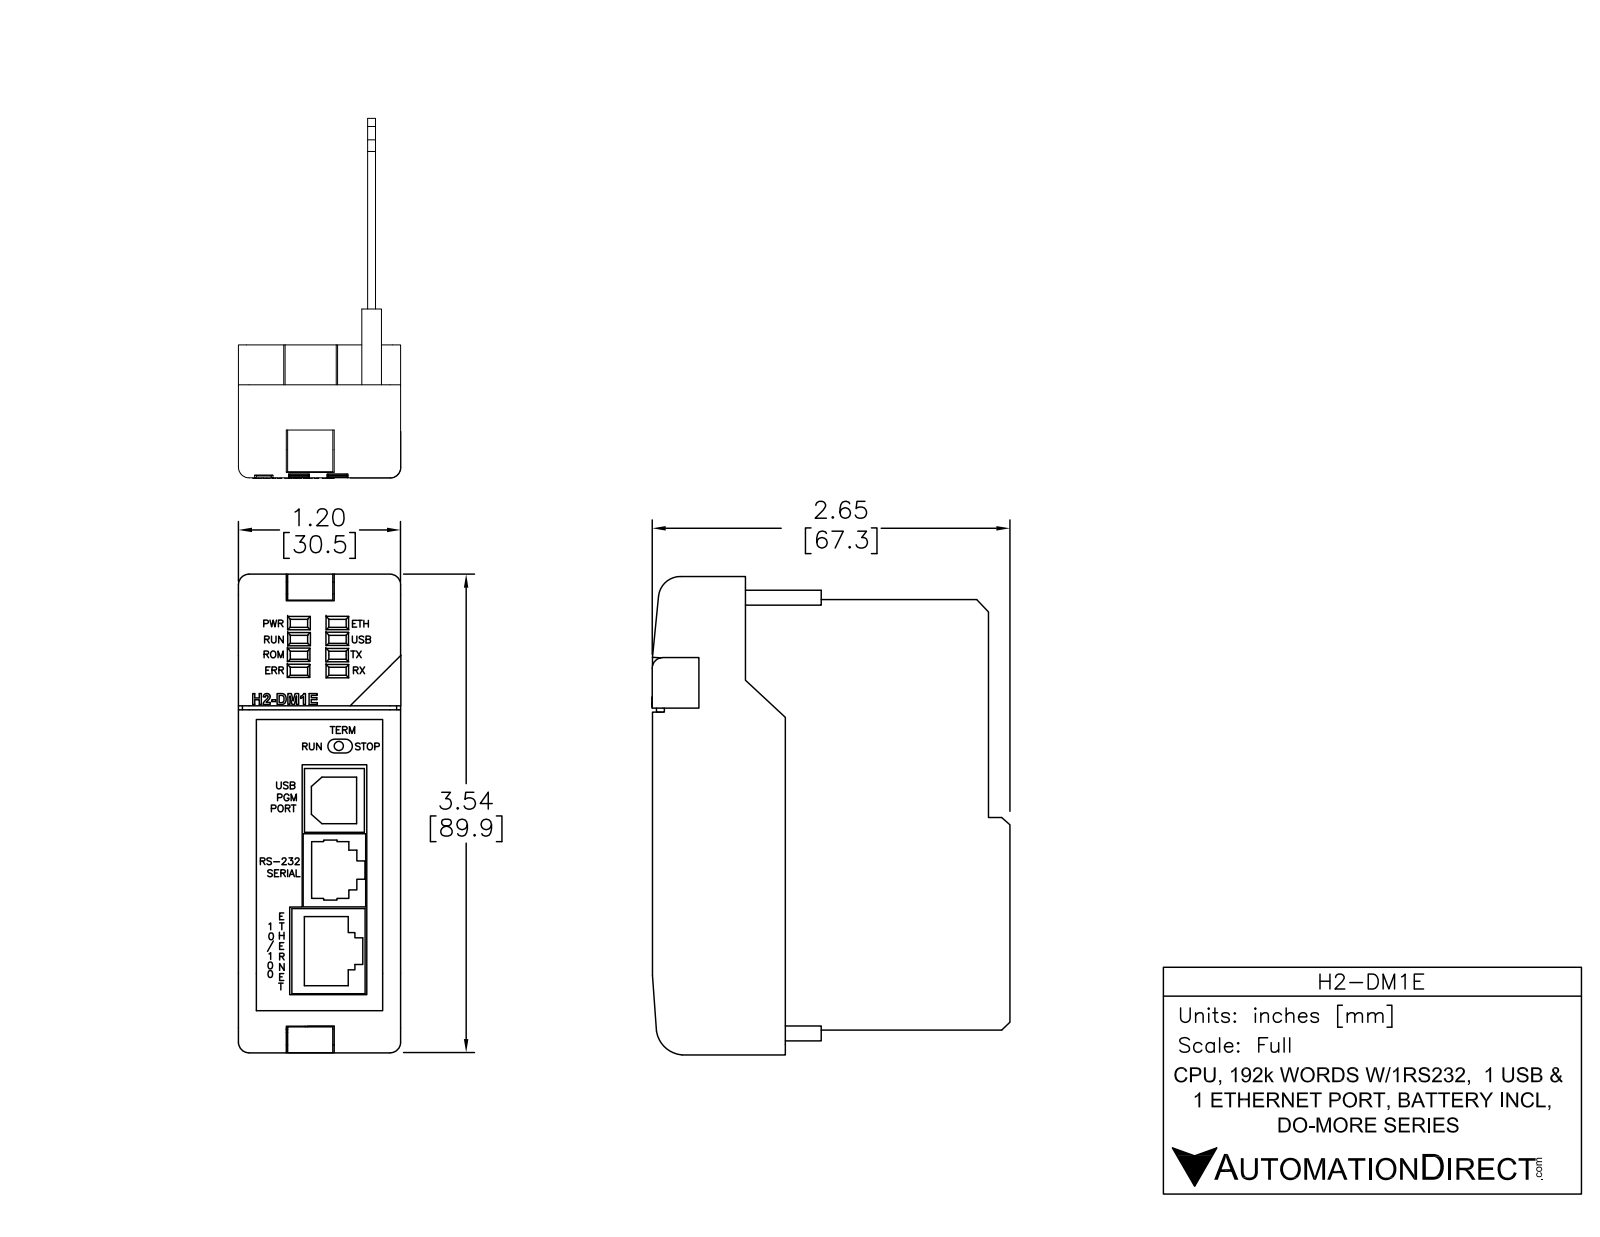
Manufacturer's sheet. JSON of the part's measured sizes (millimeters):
{"part_name": "H2-DM1E", "step_written_by": "SolidWorks 2014 (AUTOMOTIVE_DESIGN)", "units": "millimeters", "bodies": {"solids": 18, "faces": 441, "planar": 321, "cylindrical": 88, "other": 32}, "overall_size": [90, 69.19, 30.55], "volume_mm3": 24086, "surface_area_mm2": 33715, "round_bosses_or_shafts": [[1.72, 1]], "partial_cylinders_radius": [[0.5, 28], [2, 11], [0.25, 4], [1, 2], [1.3, 2], [2.62, 1], [3.79, 1], [4.12, 1]], "face_to_face_distances": [1.5, 4.72, 3.22, 6.22, 24.28, 29, 0.5, 13.75, 25.78, 30.5]}
